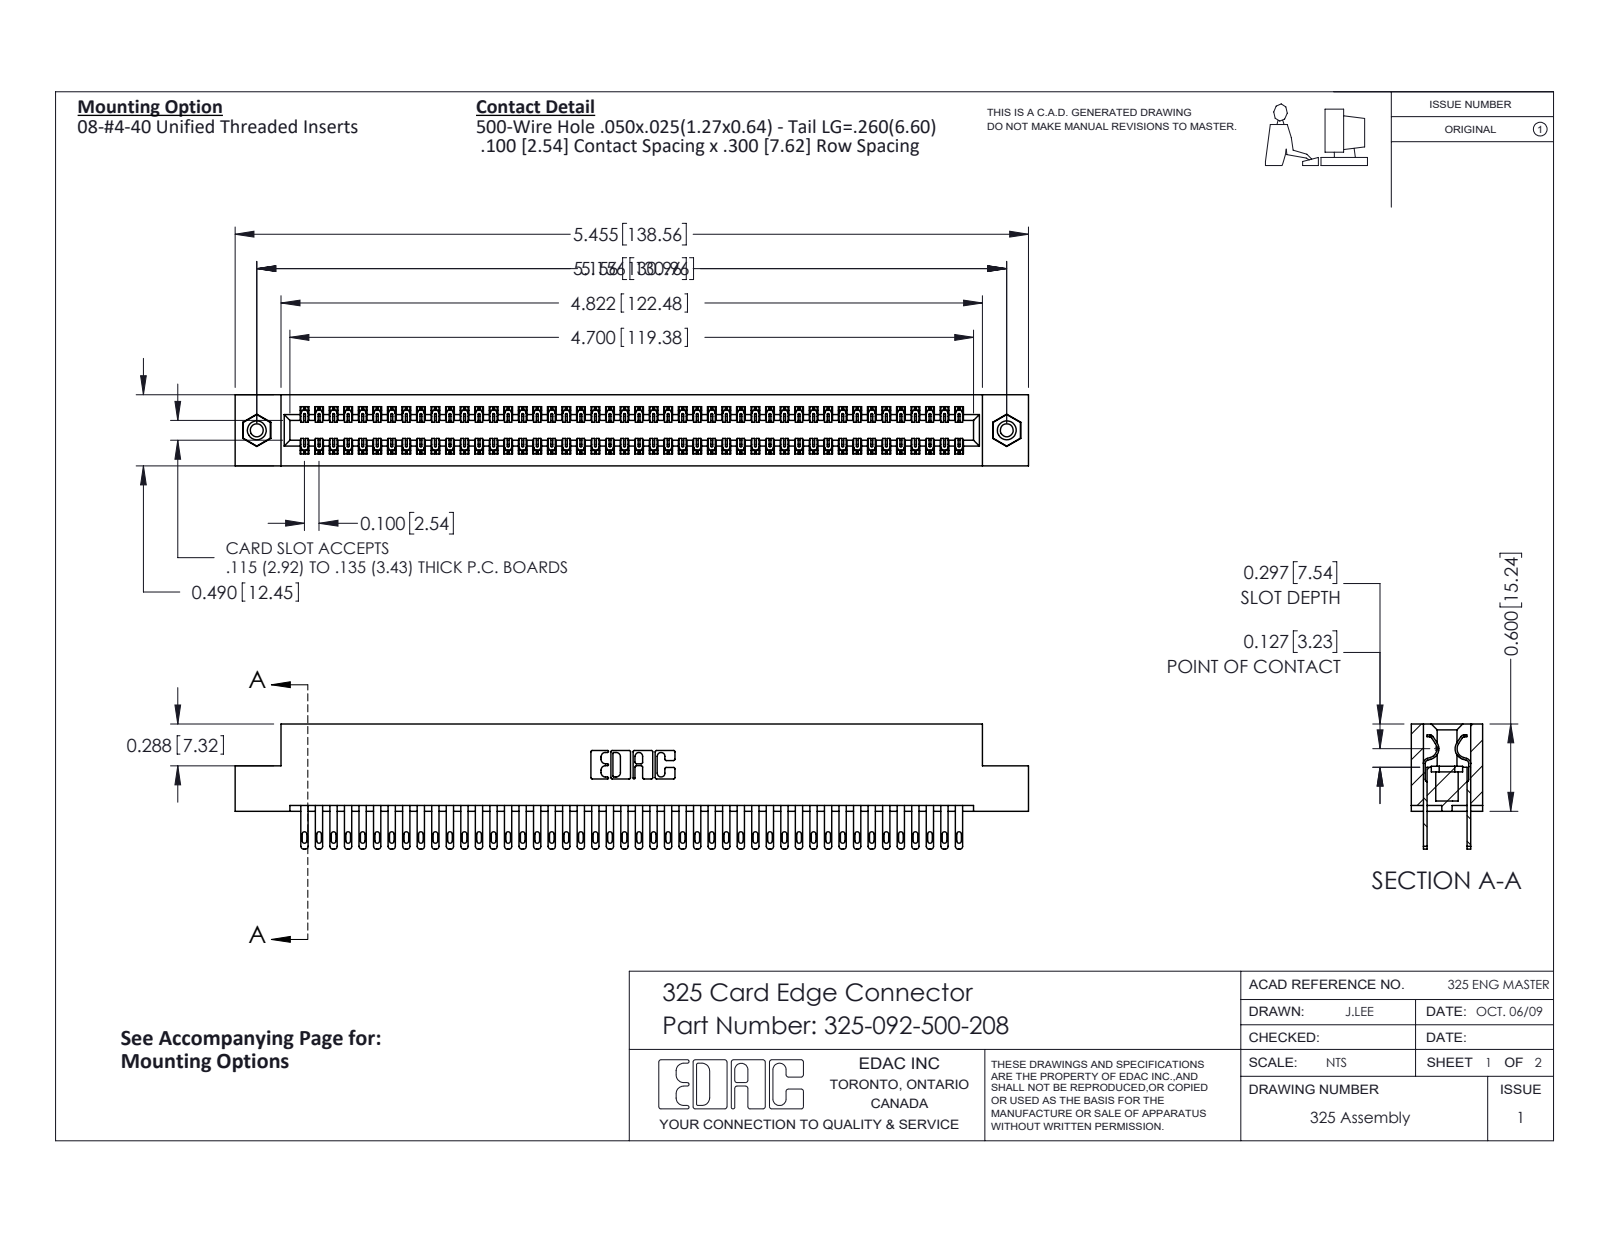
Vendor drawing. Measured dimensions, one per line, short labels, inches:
name: 325-092-500-208; 345-250-001_345-250-003-102; 325-292-001_325-293-100; 325 Part_TI
written by: SolidWorks 2016 (CONFIG_CONTROL_DESIGN)
unit: in
bodies: 95 solids, 4590 faces (2862 planar, 1712 cylindrical, 16 other)
size: 5.455 × 0.86 × 0.49
volume: 1.11 in³; area: 35.8 in²
holes: 2× ⌀0.089, 2× ⌀0.125, 2× ⌀0.16
bosses: 2× ⌀0.155
rounds: 138× R0.006, 92× R0.016, 92× R0.02, 22× R0.01, 6× R0.007, 6× R0.031, 3× R0.026, 2× R0.014
face distances: 0.083, 0.407, 0.3, 0.107, 0.383, 0.025, 0.49, 0.325, 0.275, 0.56
hole spacings: 5.156
